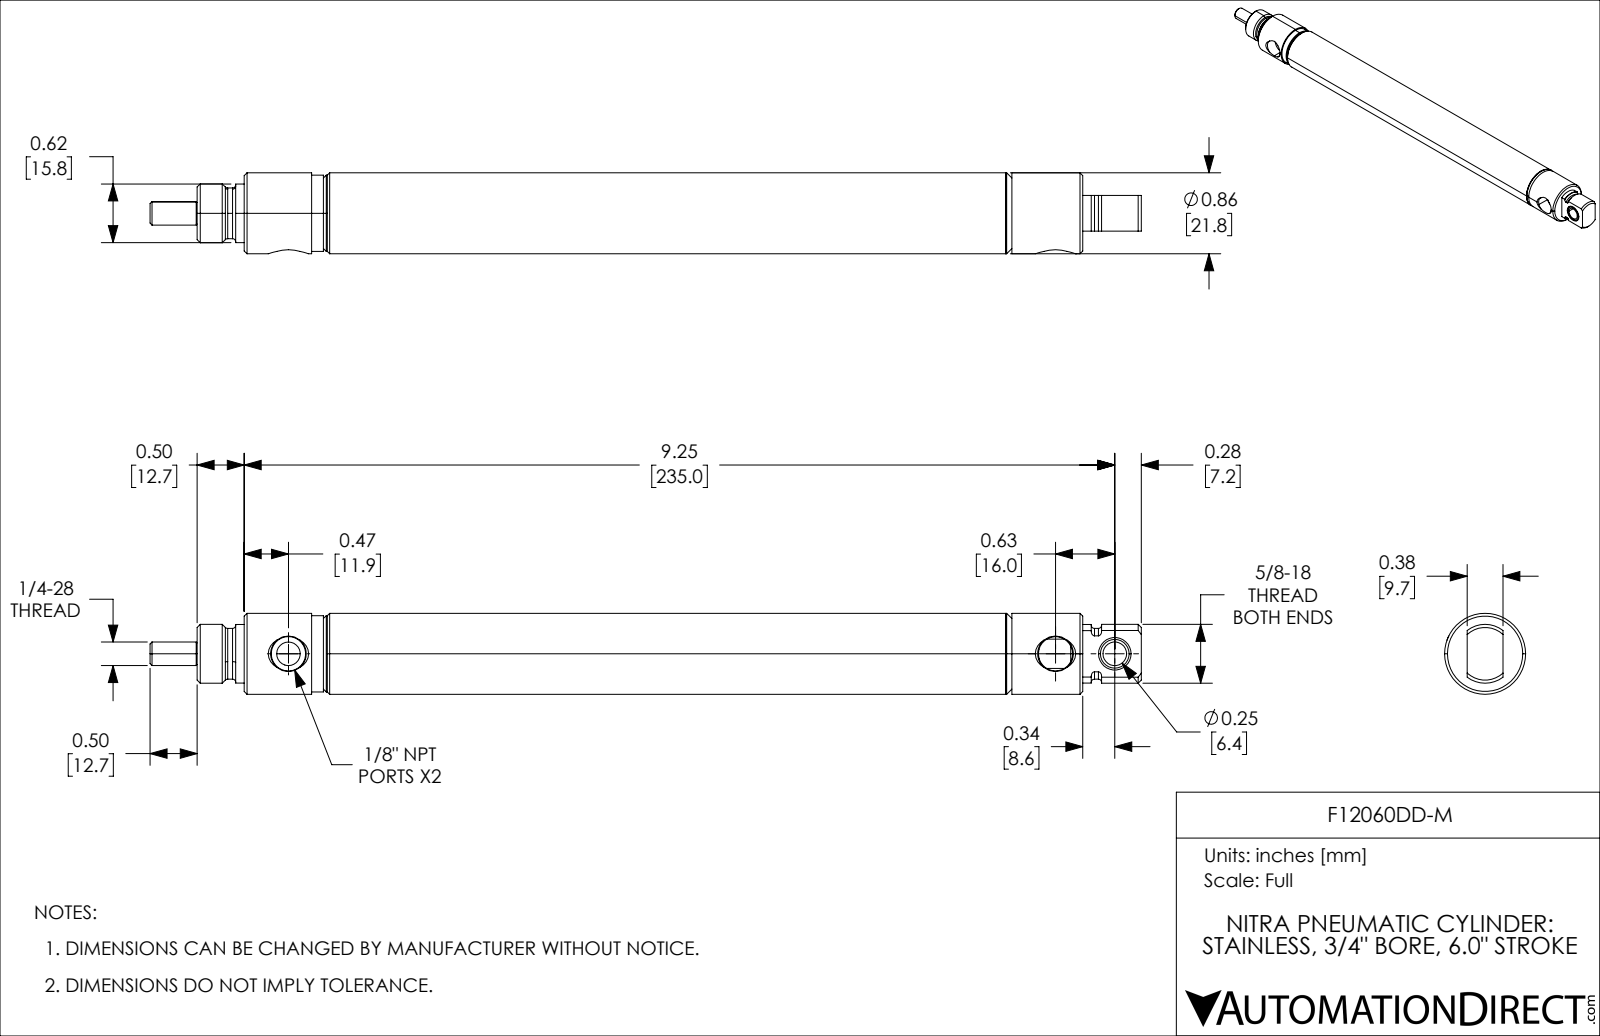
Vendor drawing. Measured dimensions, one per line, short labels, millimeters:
name: F12060DD-M; F12060DD-M_7; F12060DD-M_3; F12060DD-M_11 (+2 more)
written by: SolidWorks 2021 (CONFIG_CONTROL_DESIGN)
unit: mm
bodies: 5 solids, 158 faces (29 planar, 61 cylindrical, 68 other)
size: 267.51 × 21.84 × 21.84
volume: 46 387 mm³; area: 39 201 mm²
holes: 1× ⌀6.35, 1× ⌀6.38, 1× ⌀6.95, 1× ⌀7.92, 1× ⌀8.78, 1× ⌀9.23, 1× ⌀12.7, 1× ⌀17.83
bosses: 1× ⌀21.84, 1× ⌀20.57, 1× ⌀19.35, 1× ⌀15.88, 1× ⌀15.81, 1× ⌀13.68, 1× ⌀6.35, 1× ⌀5.84
rounds: 1× R6.84
face distances: 21.43, 40.49, 214.32, 152.4, 173.83, 198.52, 46.12, 24.69, 12.7, 9.66
hole spacings: 16, 207.01, 223.01
